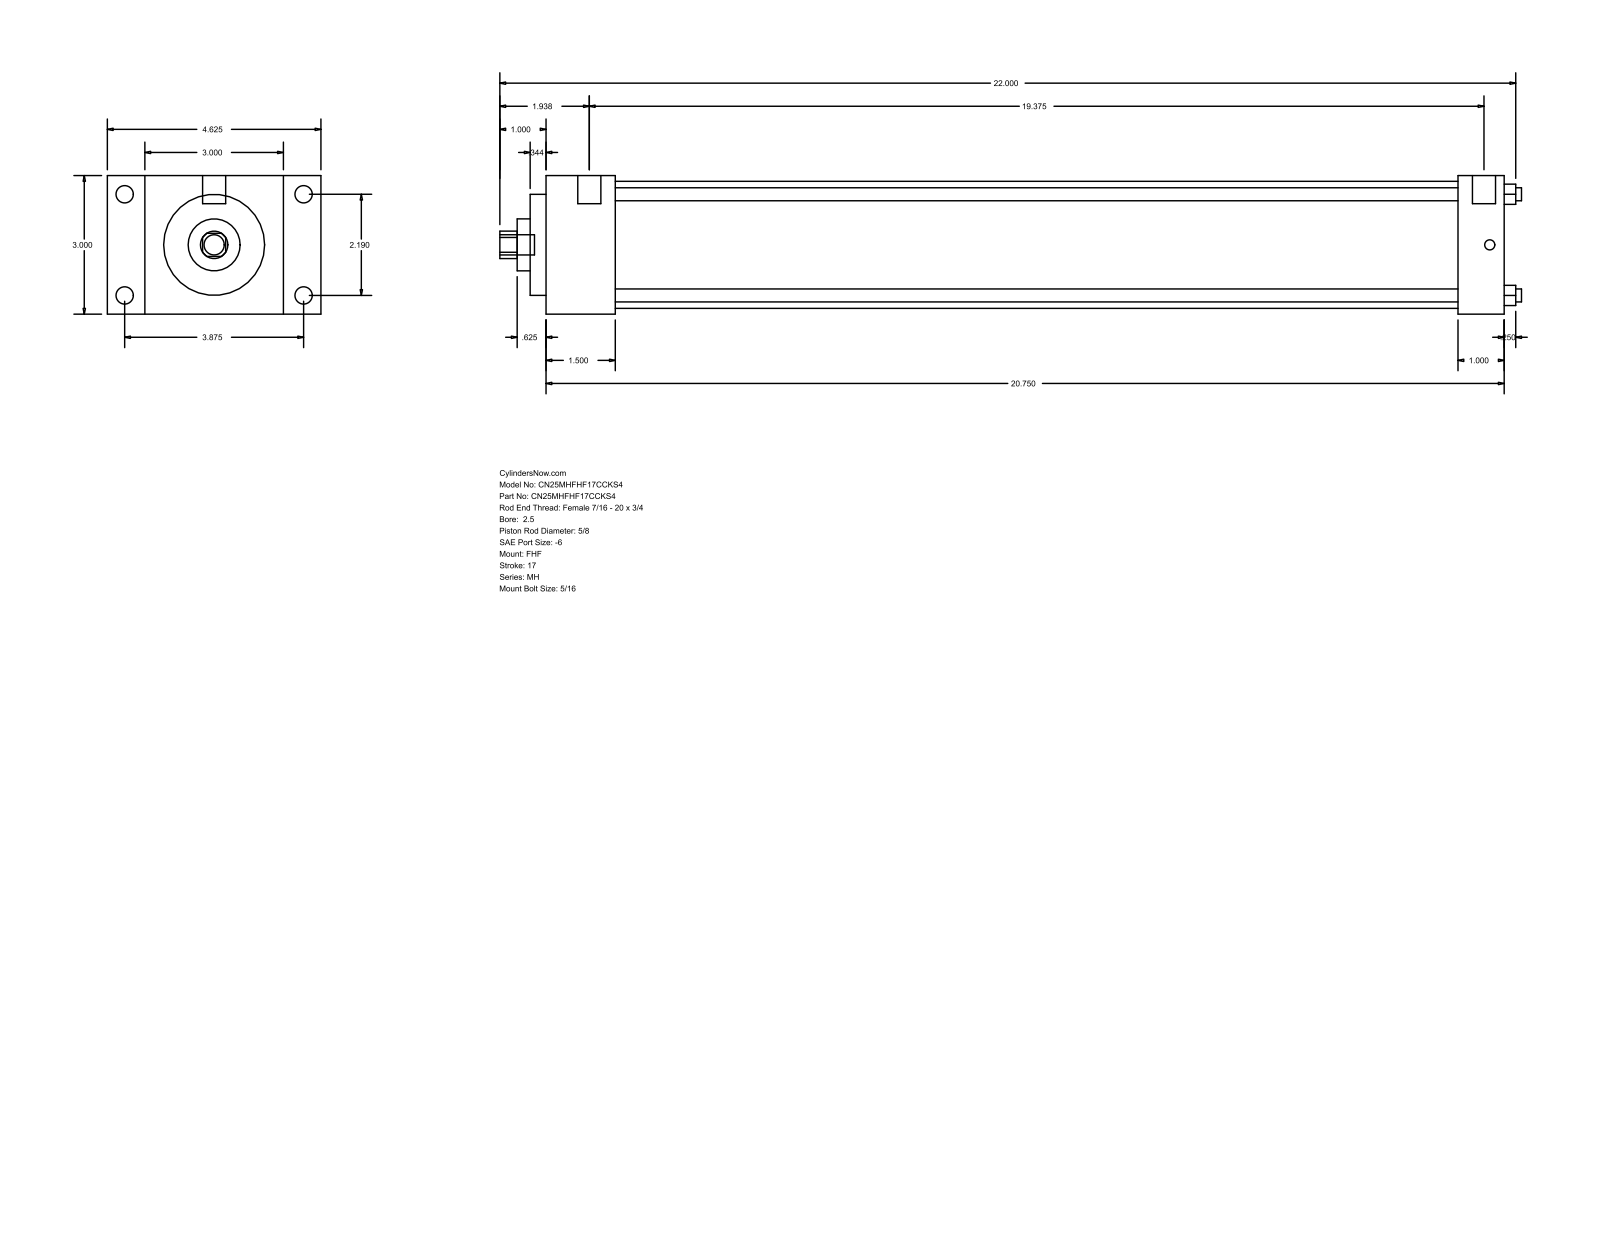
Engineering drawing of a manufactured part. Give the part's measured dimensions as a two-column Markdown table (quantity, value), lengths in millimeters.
| quantity | value |
| --- | --- |
| part name | MH_FHF__0250_0.625 |
| STEP written by | GSSL Pune (CONFIG_CONTROL_DESIGN) |
| units | millimeters |
| bodies | 0 solids, 90 faces (61 planar, 29 cylindrical, 0 other) |
| overall size | 561.98 × 117.47 × 76.2 |
| round holes (diameter × count) | 7.14 × 4, 15.88 × 1, 28.57 × 1, 55.55 × 1, 69.85 × 1 |
| round bosses / shafts (diameter × count) | 9.53 × 4, 5.56 × 4, 12.7 × 2, 11.11 × 1 |
| partial cylindrical surfaces (radius × count) | 7.54 × 1 |
| main face-to-face distances | 76.2, 527.05, 38.1, 488.95, 20.64, 96.84, 117.48, 25.4, 501.65, 463.55 |
| hole center spacings | 39.33, 55.62, 78.66 |
